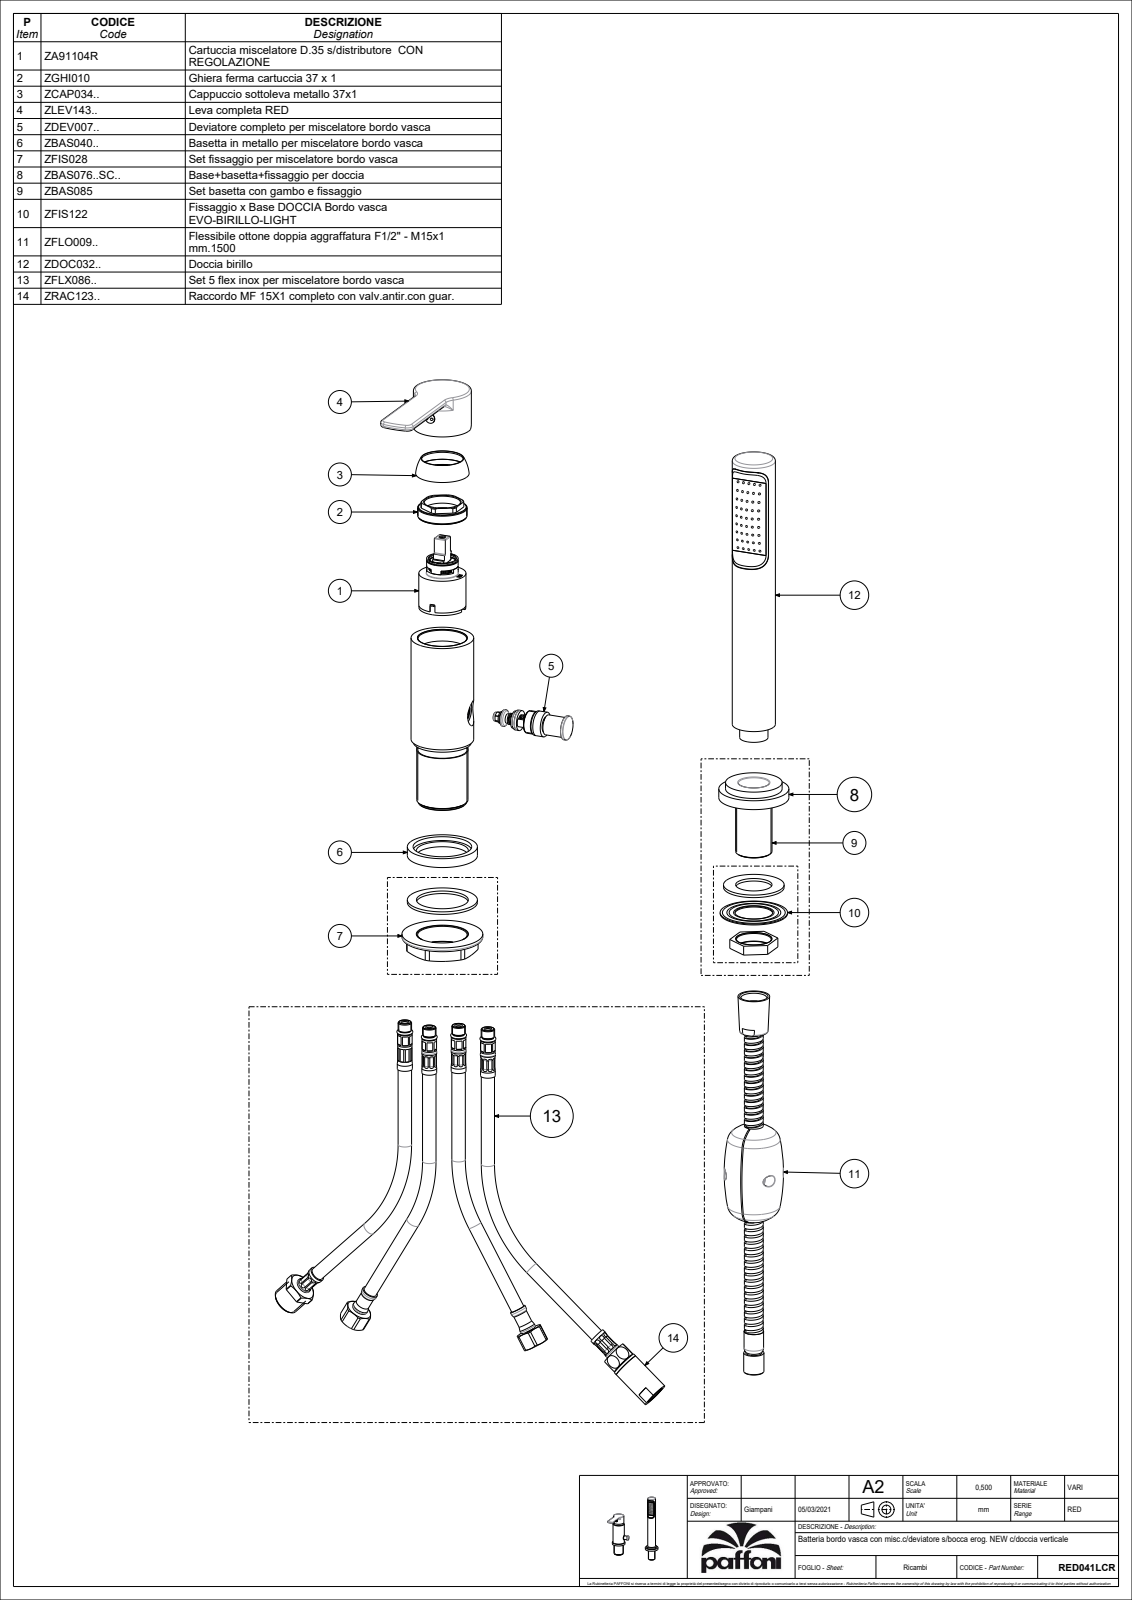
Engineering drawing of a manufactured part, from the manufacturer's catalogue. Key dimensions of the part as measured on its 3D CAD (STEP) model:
Part name (STEP PRODUCT): RED041LCR
STEP written by: CREO PARAMETRIC BY PTC INC, 2020044 (CONFIG_CONTROL_DESIGN)
Units: millimetres
Bodies: 3 solids, 1405 faces (668 planar, 468 cylindrical, 269 other)
Overall size (bounding box): 223 × 202 × 111
Volume: 224 438 mm³ · Surface area: 116 904 mm²
Round holes (diameter × count): ⌀1.5 ×45, ⌀7 ×6, ⌀3.3 ×2, ⌀4 ×2, ⌀4.5 ×2, ⌀49.2 ×2, ⌀3 ×1, ⌀3.1 ×1, ⌀4.3 ×1, ⌀5 ×1, ⌀6 ×1, ⌀7.2 ×1
Round bosses / shafts (diameter × count): ⌀52 ×2, ⌀44.2 ×2, ⌀46.5 ×1, ⌀43 ×1, ⌀42 ×1, ⌀38 ×1, ⌀35 ×1, ⌀34.8 ×1
Partial cylindrical surfaces — rounded edges, fillets, slot ends (radius × count): R0.5 ×66, R0.15 ×11, R0.3 ×4, R1.5 ×4, R10 ×4, R1 ×2, R5 ×2, R7.8 ×2
Main face-to-face distances: 119.1, 2, 4.5, 5, 10, 123.6, 7, 221, 112.1, 116.6
Hole centre spacings: 7.91, 13.76, 20.01, 6.5, 13, 26.39, 4.5, 19.5
